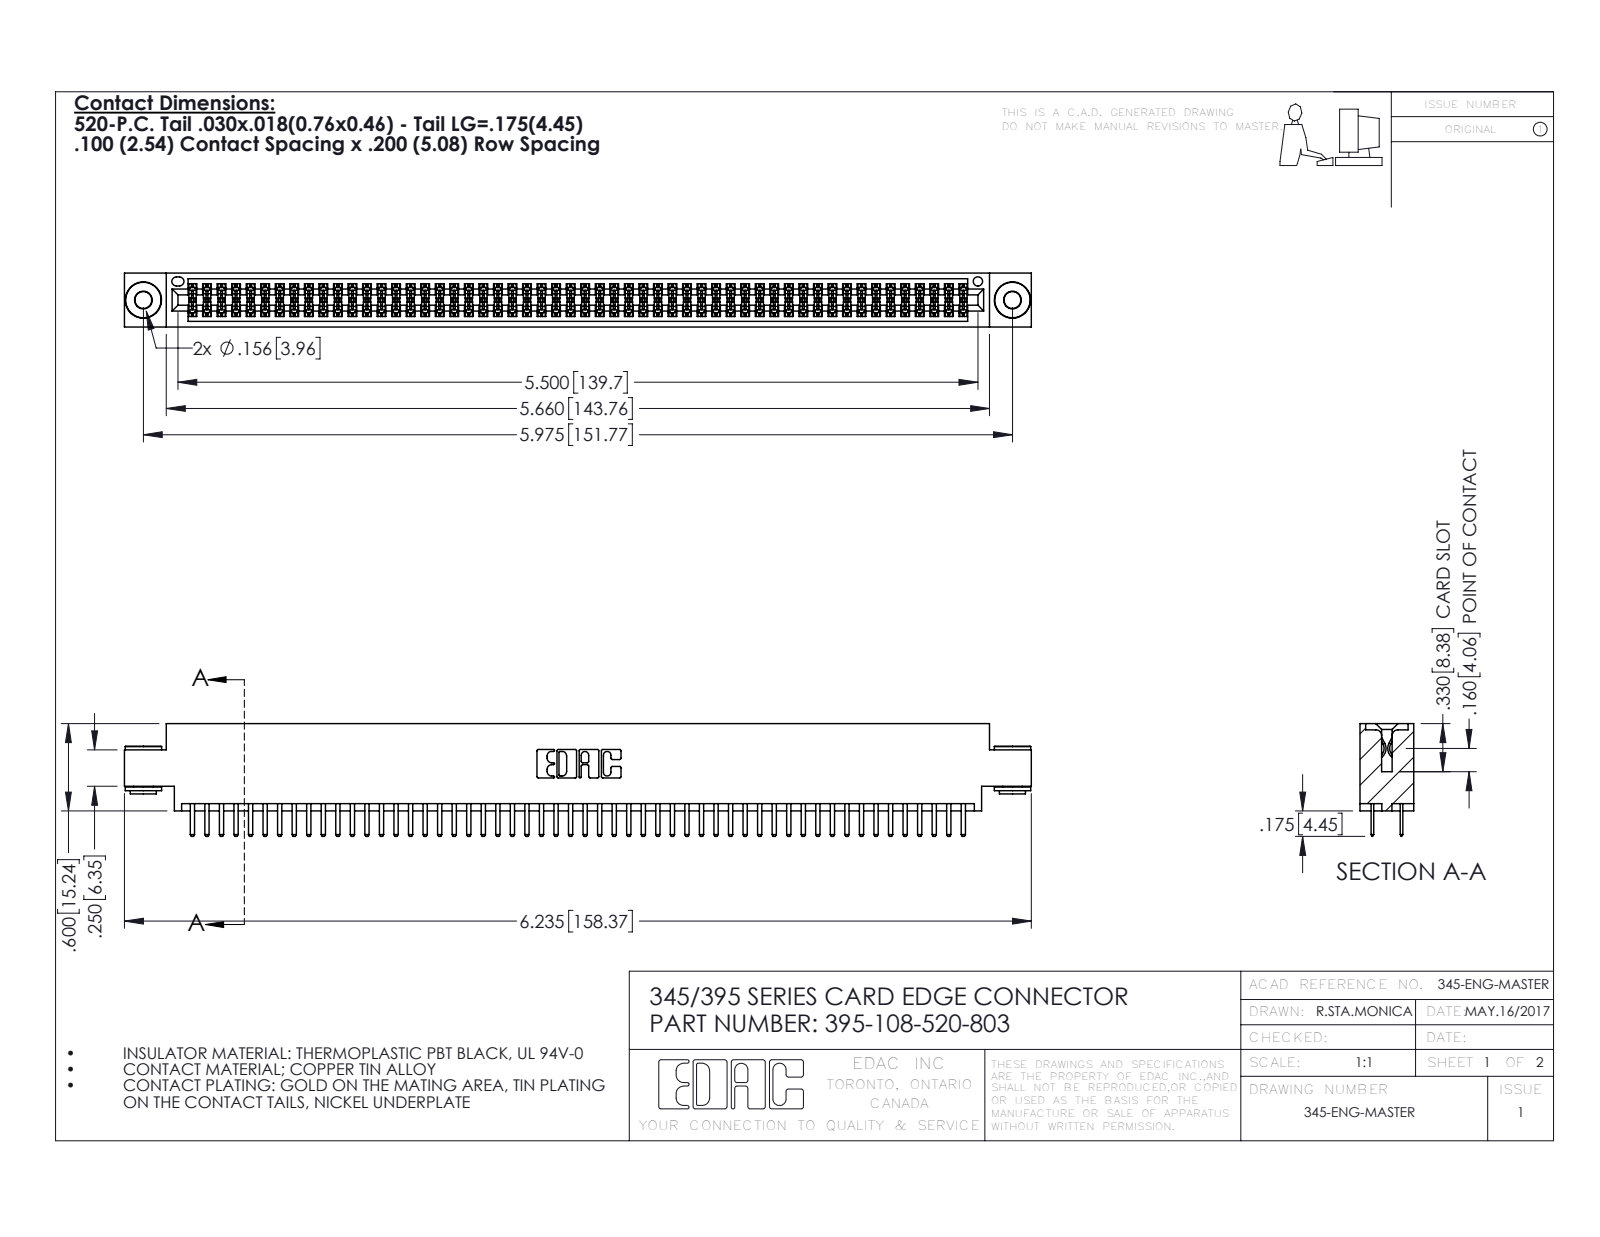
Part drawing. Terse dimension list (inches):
name: 395-108-520-803; 345-292-001_345-293-120; 345 Part_0.170 Offset - 0.156 Dia-TH; 345-250-002_345-250-002-102
written by: SolidWorks 2016 (CONFIG_CONTROL_DESIGN)
unit: in
bodies: 111 solids, 6000 faces (3874 planar, 2118 cylindrical, 8 other)
size: 6.235 × 0.775 × 0.37
volume: 0.937 in³; area: 35.92 in²
holes: 2× ⌀0.116, 2× ⌀0.156, 1× ⌀0.064
bosses: 2× ⌀0.25, 2× ⌀0.18, 2× ⌀0.136
rounds: 162× R0.006, 112× R0.01, 22× R0.01, 6× R0.007, 6× R0.031, 3× R0.026, 2× R0.014, 2× R0.019
face distances: 0.072, 0.298, 0.2, 0.37, 0.098, 0.272, 0.025, 0.225, 0.022, 0.175
hole spacings: 0.27, 5.739, 5.975
